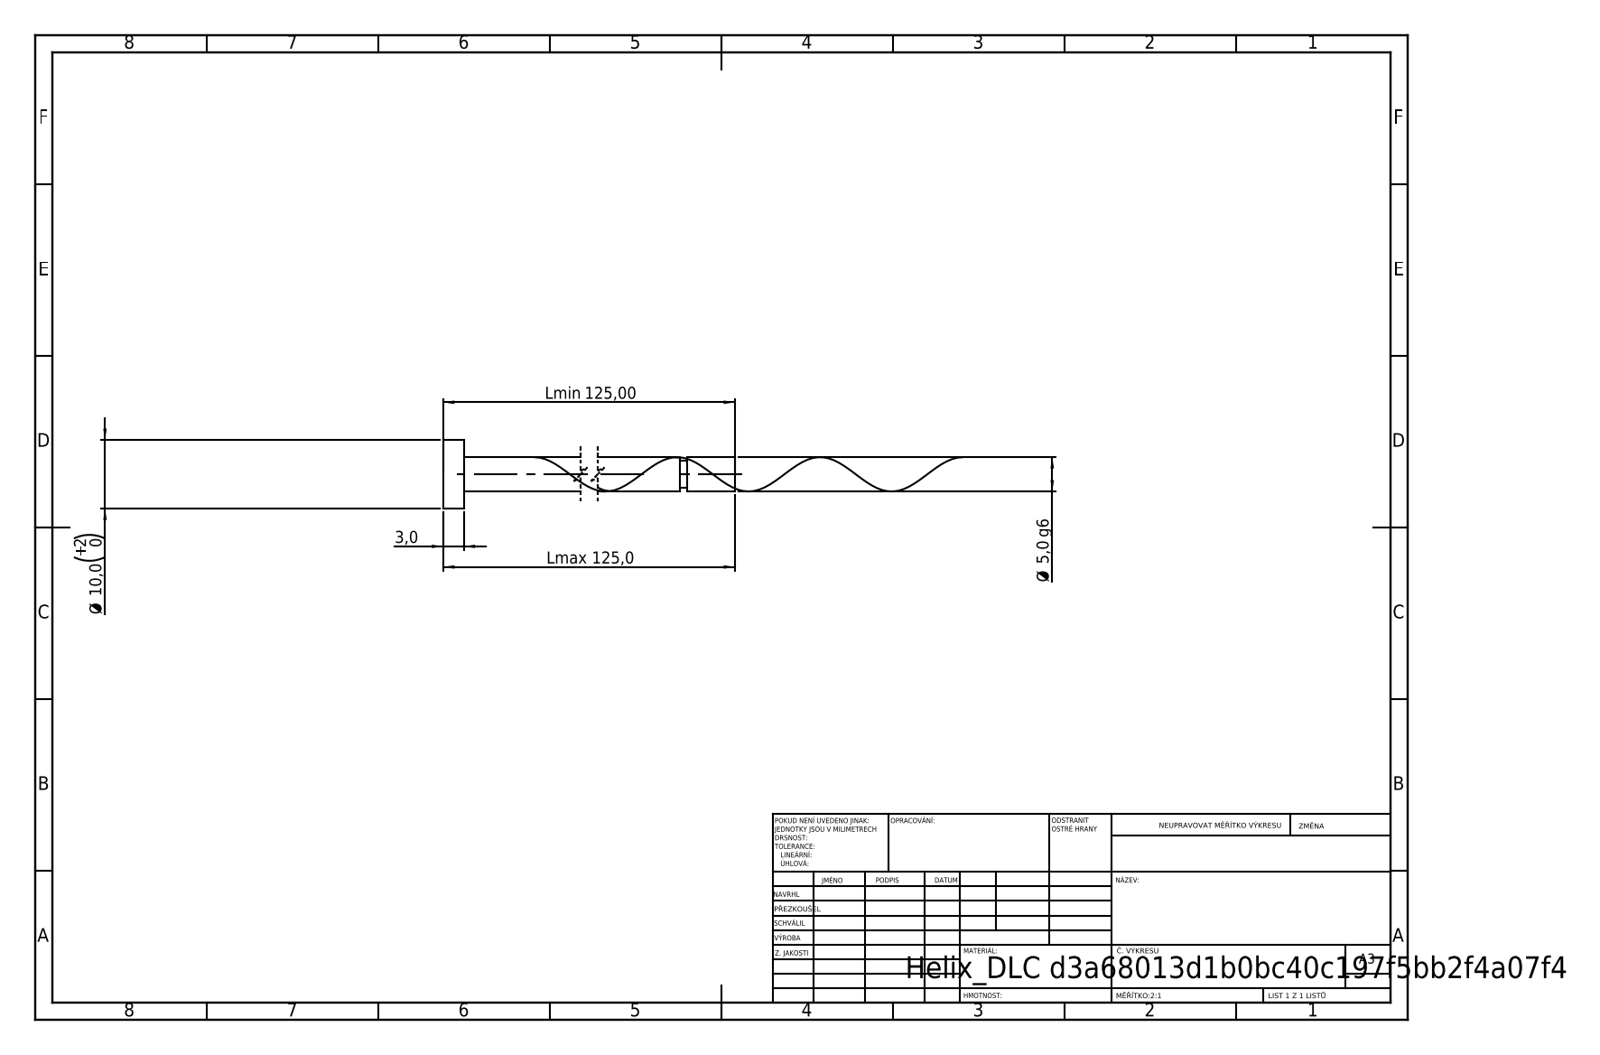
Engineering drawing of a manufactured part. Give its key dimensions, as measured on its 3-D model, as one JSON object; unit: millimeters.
{"step_written_by": "SolidWorks 2019 (CONFIG_CONTROL_DESIGN)", "units": "millimeters", "bodies": {"solids": 1, "faces": 21, "planar": 6, "cylindrical": 14, "other": 1}, "overall_size": [125, 10, 10], "volume_mm3": 2601, "surface_area_mm2": 2219, "round_bosses_or_shafts": [[10, 1], [5, 1], [4, 1]], "face_to_face_distances": [3, 125, 122, 118, 115, 7, 117, 114, 1, 8]}
